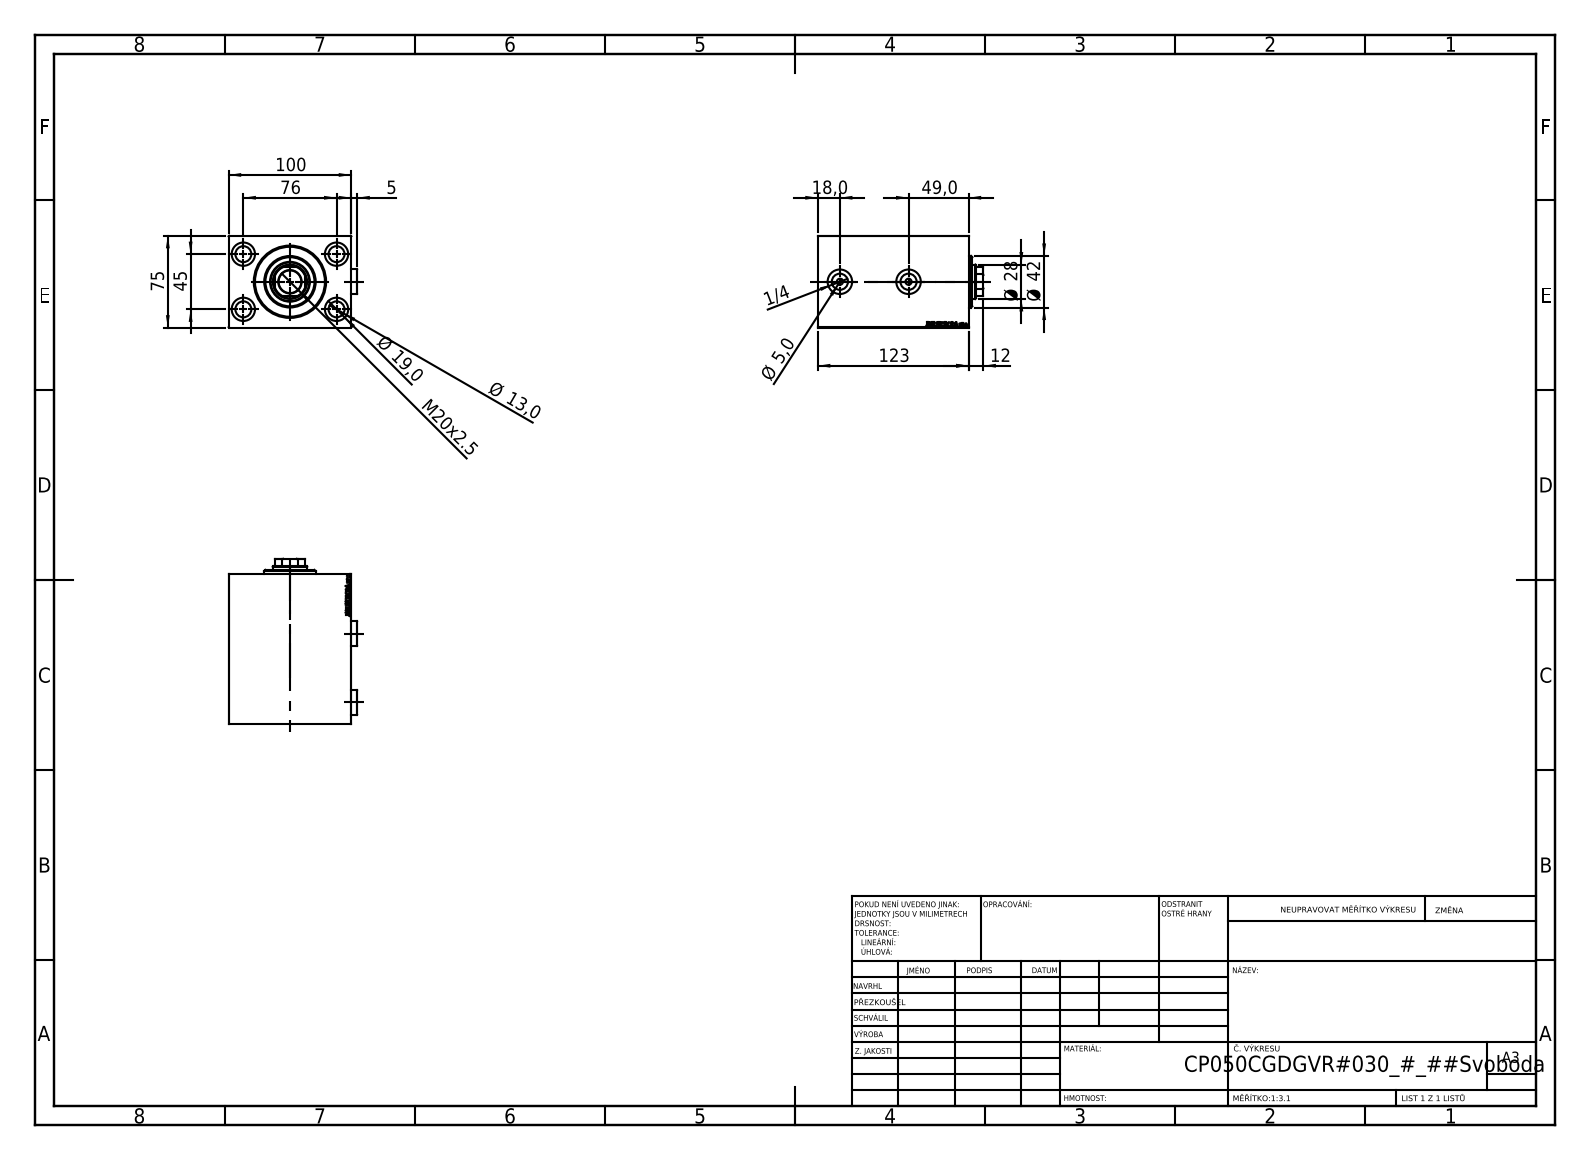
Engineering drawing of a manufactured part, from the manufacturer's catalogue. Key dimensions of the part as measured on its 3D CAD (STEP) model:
Part name (STEP PRODUCT): V450CP_C; V450CP_B_VCP; PLUG; V450CP_VC_B
STEP written by: SolidWorks 2019 (CONFIG_CONTROL_DESIGN)
Units: millimetres
Bodies: 5 solids, 943 faces (449 planar, 92 cylindrical, 402 other)
Overall size (bounding box): 135 × 104.9 × 75
Volume: 795 766 mm³ · Surface area: 136 684 mm²
Round holes (diameter × count): ⌀13 ×4, ⌀19 ×4, ⌀4 ×2, ⌀5 ×2, ⌀9.73 ×2, ⌀13.16 ×2, ⌀15 ×2, ⌀20 ×2, ⌀18.5 ×1, ⌀28 ×1, ⌀31.5 ×1, ⌀32.5 ×1
Round bosses / shafts (diameter × count): ⌀42 ×1
Partial cylindrical surfaces — rounded edges, fillets, slot ends (radius × count): R13.5 ×1
Main face-to-face distances: 75, 100, 123, 14, 109, 30, 74, 44, 49, 60
Hole centre spacings: 44.16, 45, 76, 88.32, 42.55, 56
